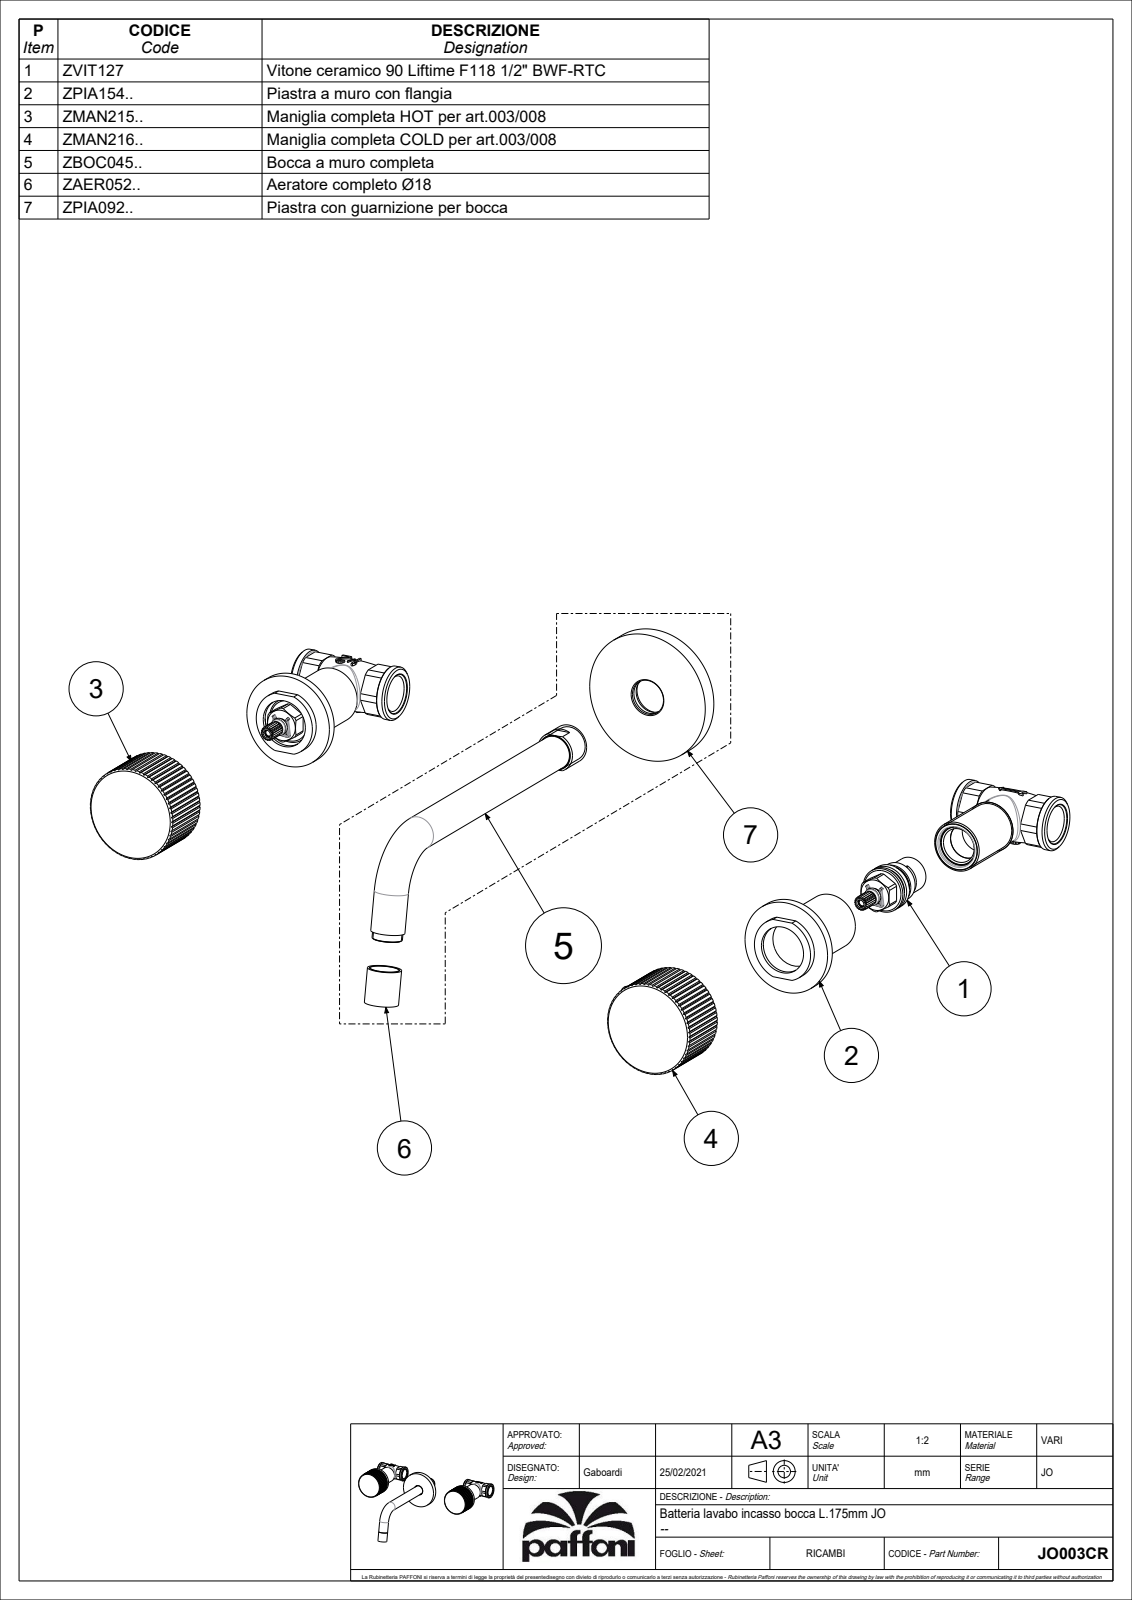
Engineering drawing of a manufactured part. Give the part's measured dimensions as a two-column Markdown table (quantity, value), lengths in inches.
| quantity | value |
| --- | --- |
| part name | JO003CR |
| STEP written by | CREO PARAMETRIC BY PTC INC, 2020044 (CONFIG_CONTROL_DESIGN) |
| units | inches |
| bodies | 6 solids, 1471 faces (653 planar, 586 cylindrical, 232 other) |
| overall size | 9.843 × 6.44 × 3.928 |
| volume | 6.971 in³ |
| surface area | 144.2 in² |
| round holes (diameter × count) | 0.02 × 51, 0.591 × 4, 0.118 × 2, 0.165 × 2, 0.217 × 2, 0.315 × 2, 1.004 × 2, 1.417 × 2, 1.614 × 2, 1.819 × 2, 1.85 × 2, 0.433 × 1 |
| round bosses / shafts (diameter × count) | 1.969 × 2, 1.732 × 2, 1.622 × 2, 1.181 × 2, 0.945 × 2, 0.866 × 2, 0.843 × 2, 0.709 × 2 |
| partial cylindrical surfaces (radius × count) | 0.008 × 52, 0.02 × 24, 0.039 × 4, 0.37 × 2, 0.528 × 2, 0.167 × 1 |
| main face-to-face distances | 0.079, 0.354, 0.276, 0.197, 0.157, 0.878, 0.799, 1.327, 1.13, 1.051 |
| hole center spacings | 0.132, 0.059, 0.083, 0.132, 0.187, 0.213, 0.187, 0.167 |
